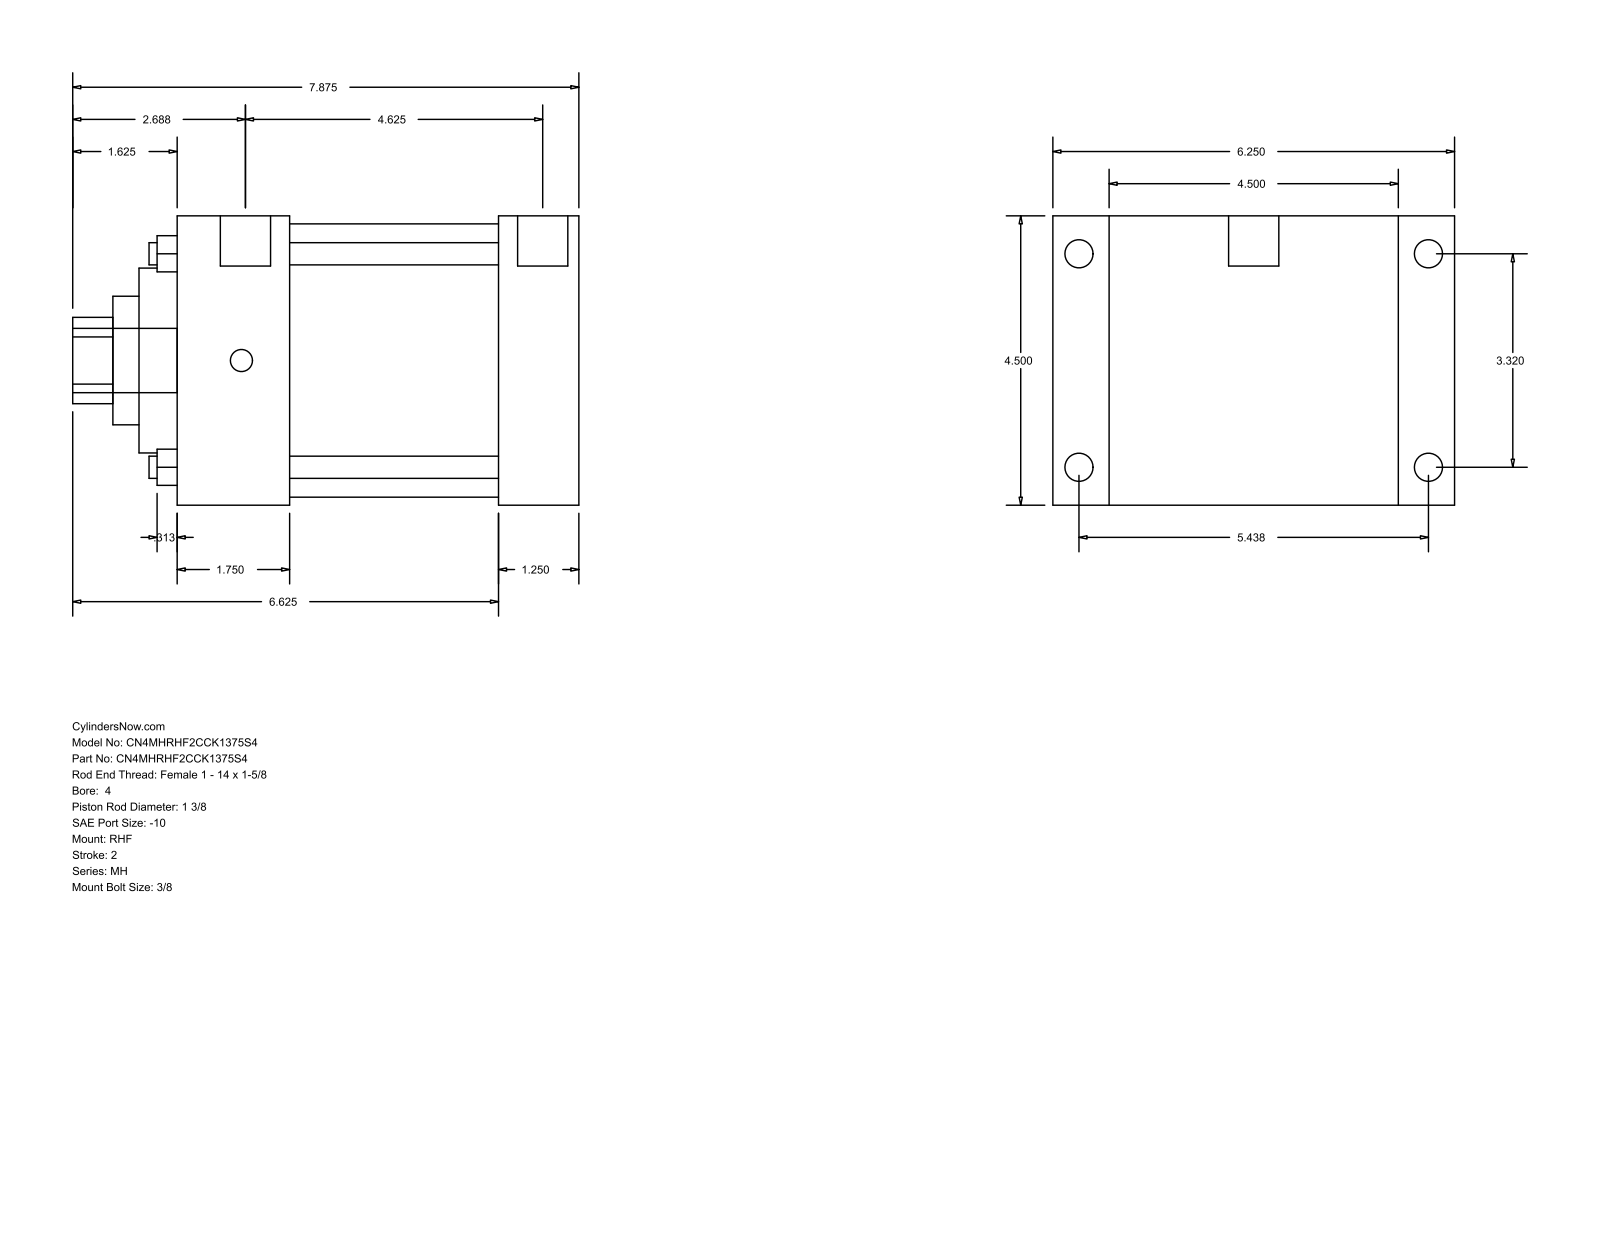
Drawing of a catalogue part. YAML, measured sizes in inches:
part_name: "MH_RHF__0400_1.375"
step_written_by: "GSSL Pune (CONFIG_CONTROL_DESIGN)"
units: inches
bodies: {solids: 0, faces: 90, planar: 61, cylindrical: 29, other: 0}
overall_size: [7.875, 6.25, 4.5]
round_holes:
  - {diameter: 0.345, count: 4}
  - {diameter: 1.375, count: 1}
  - {diameter: 2, count: 1}
  - {diameter: 2.875, count: 1}
  - {diameter: 4.25, count: 1}
round_bosses_or_shafts:
  - {diameter: 0.438, count: 4}
  - {diameter: 0.344, count: 4}
  - {diameter: 0.781, count: 2}
  - {diameter: 1, count: 1}
partial_cylinders:
  - {radius: 0.672, count: 1}
face_to_face_distances: [4.5, 6.25, 5, 1.25, 0.875, 5.375, 1.75, 3.25, 4.5, 0.594]
hole_center_spacings: [2.347, 3.32, 4.695]
